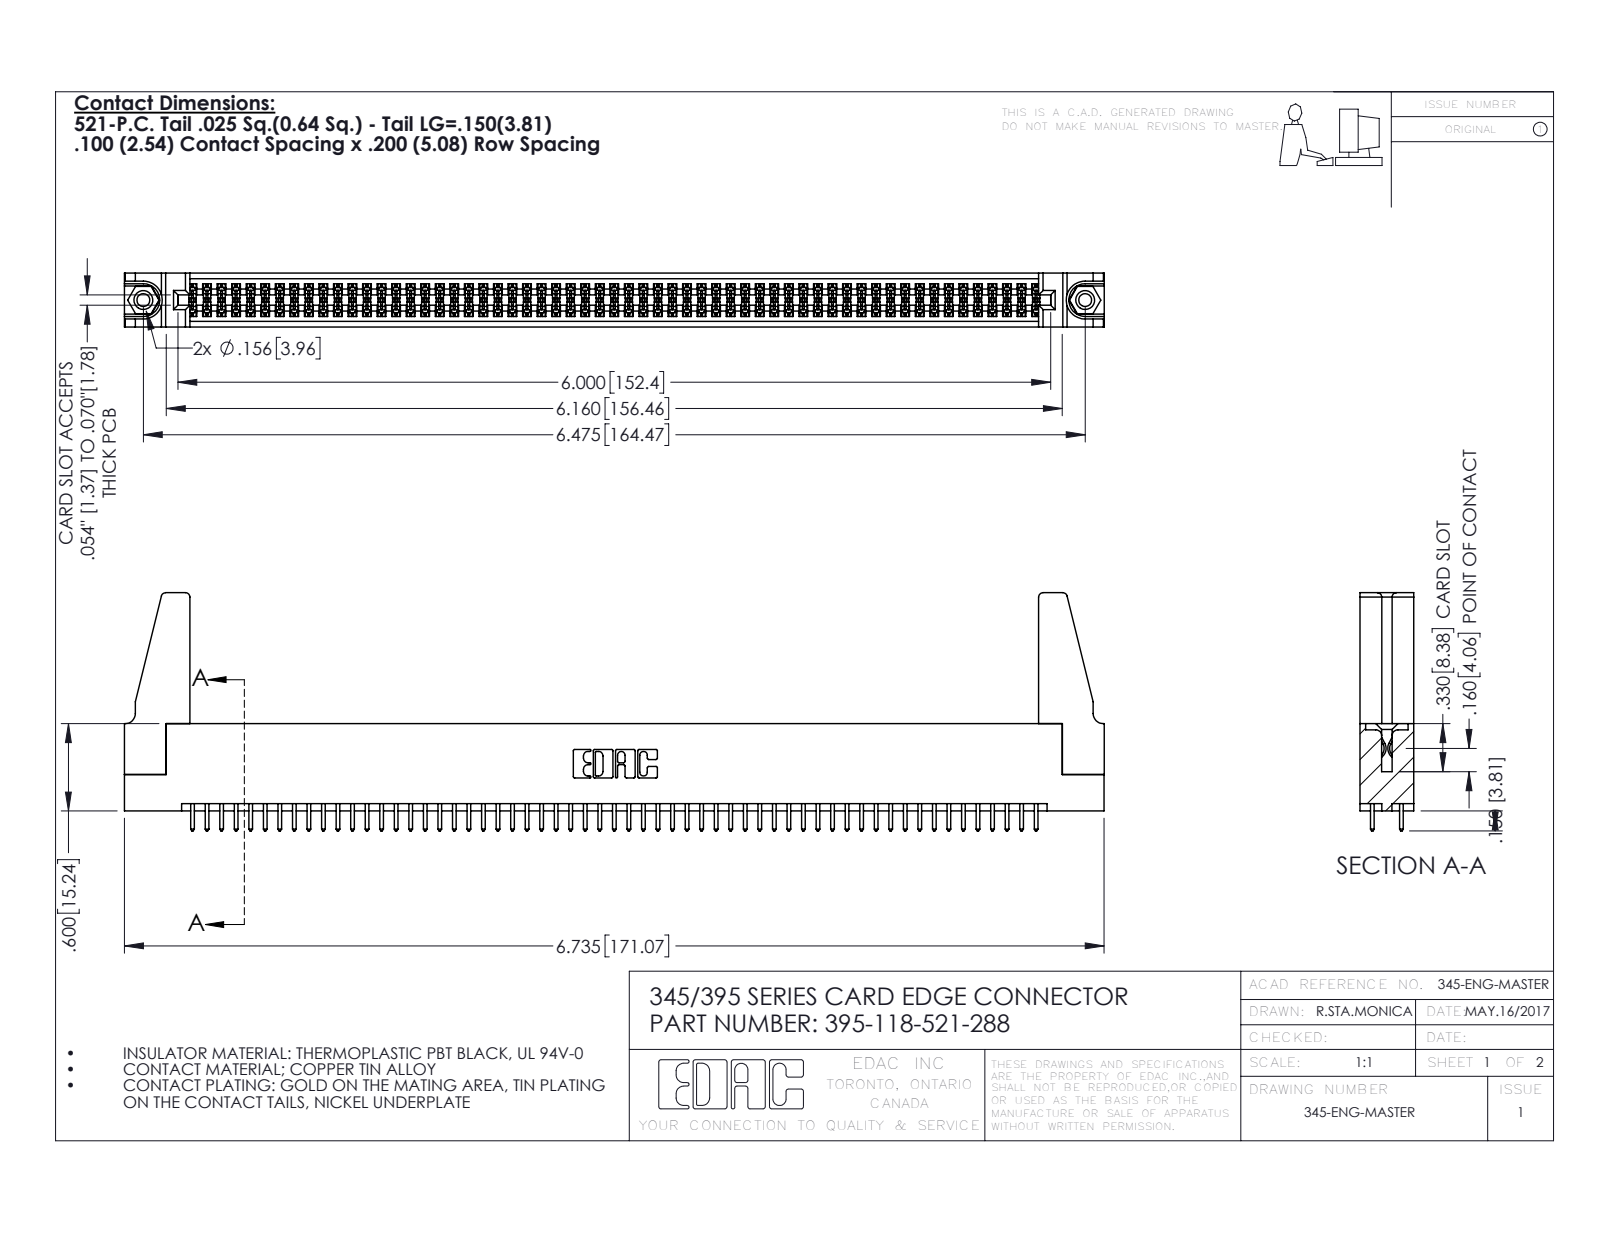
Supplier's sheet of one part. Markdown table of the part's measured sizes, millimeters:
| quantity | value |
| --- | --- |
| part name | 345-220-078_345-220-088; 395-118-521-288; 345-250-001_345-250-001-102; 345 Part_Flush Mounting Lugs - 0.156 Dia-TH (+1 more) |
| STEP written by | SolidWorks 2016 (CONFIG_CONTROL_DESIGN) |
| units | millimeters |
| bodies | 123 solids, 6150 faces (4046 planar, 2088 cylindrical, 16 other) |
| overall size | 171.1 × 41.6 × 9.4 |
| volume | 19 980 mm³ |
| surface area | 27 860 mm² |
| round holes (diameter × count) | 2.3 × 2, 3.2 × 2, 4 × 2, 1.6 × 1 |
| round bosses / shafts (diameter × count) | 3.9 × 2 |
| partial cylindrical surfaces (radius × count) | 0.2 × 177, 0.3 × 118, 0.3 × 22, 0.8 × 8, 0.2 × 6, 0.8 × 6, 0.7 × 3, 0.4 × 2 |
| main face-to-face distances | 1.8, 7.6, 9.4, 5.1, 2.5, 6.9, 0.6, 5.7, 4.4, 3.8 |
| hole center spacings | 6.9, 158.5, 164.5 |
